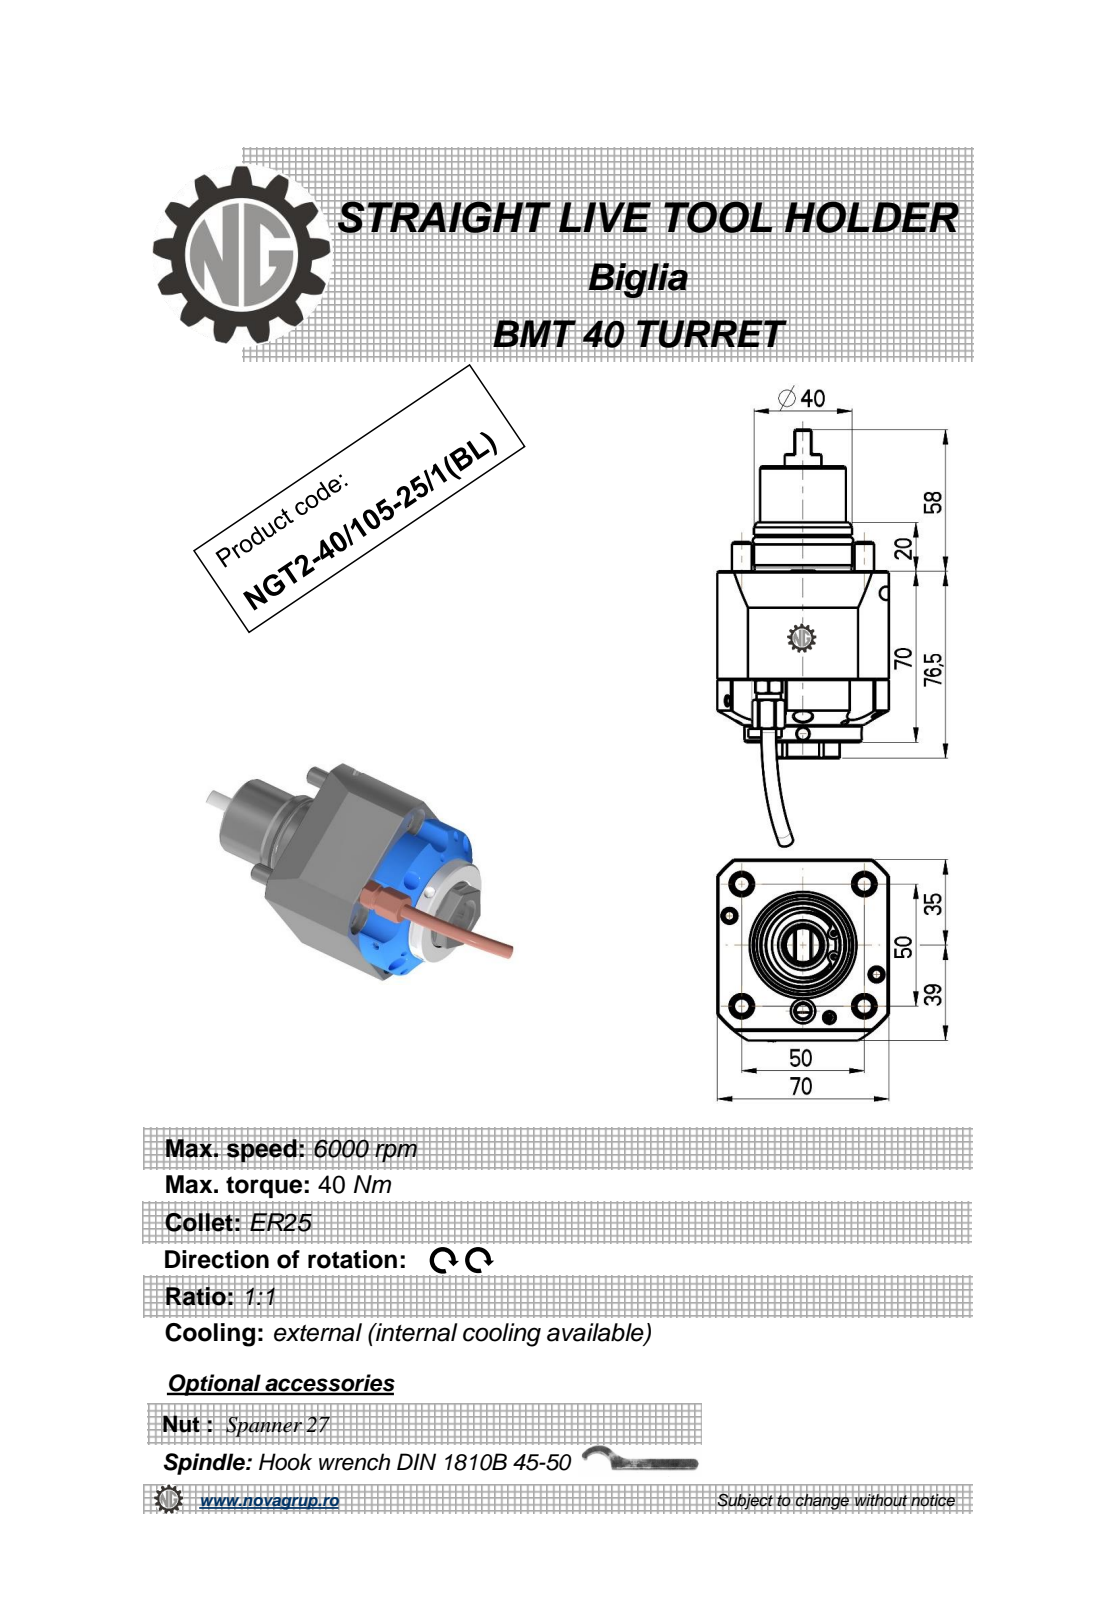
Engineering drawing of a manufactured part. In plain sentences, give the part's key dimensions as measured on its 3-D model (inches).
The part is named "NGT2_40_105_25_1_BL". Its 3-D file was written by "PRO/ENGINEER BY PARAMETRIC TECHNOLOGY CORPORATION, 2010280 (CONFIG_CONTROL_DESIGN)". It is 1 solid with 236 faces: 75 planar, 81 cylindrical and 80 other. Overall it measures 6.719 by 2.927 by 2.756 inches. Its volume is 21.16 cubic inches and its surface area 61.09 square inches. Round holes: 2 of diameter 0.157, 2 of diameter 0.197, 1 of diameter 0.236, 1 of diameter 0.709, 1 of diameter 1.043. Round bosses or shafts: 4 of diameter 0.315, 2 of diameter 0.236, 1 of diameter 1.89, 1 of diameter 1.575, 1 of diameter 1.551, 1 of diameter 1.394, 1 of diameter 1.378, 1 of diameter 0.591. Partial cylindrical surfaces (rounded edges, fillets, slot ends): 5 of radius 0.276, 2 of radius 0.031, 1 of radius 0.246, 1 of radius 0.266, 1 of radius 0.591, 1 of radius 1.378, 1 of radius 1.772. The main face-to-face distances are 2.756, 2.913, 1.752, 1.004, 3.445, 1.693, 4.449, 0.276, 2.48, 1.26. The hole center spacings are 0.6, 1.063, 1.411.
